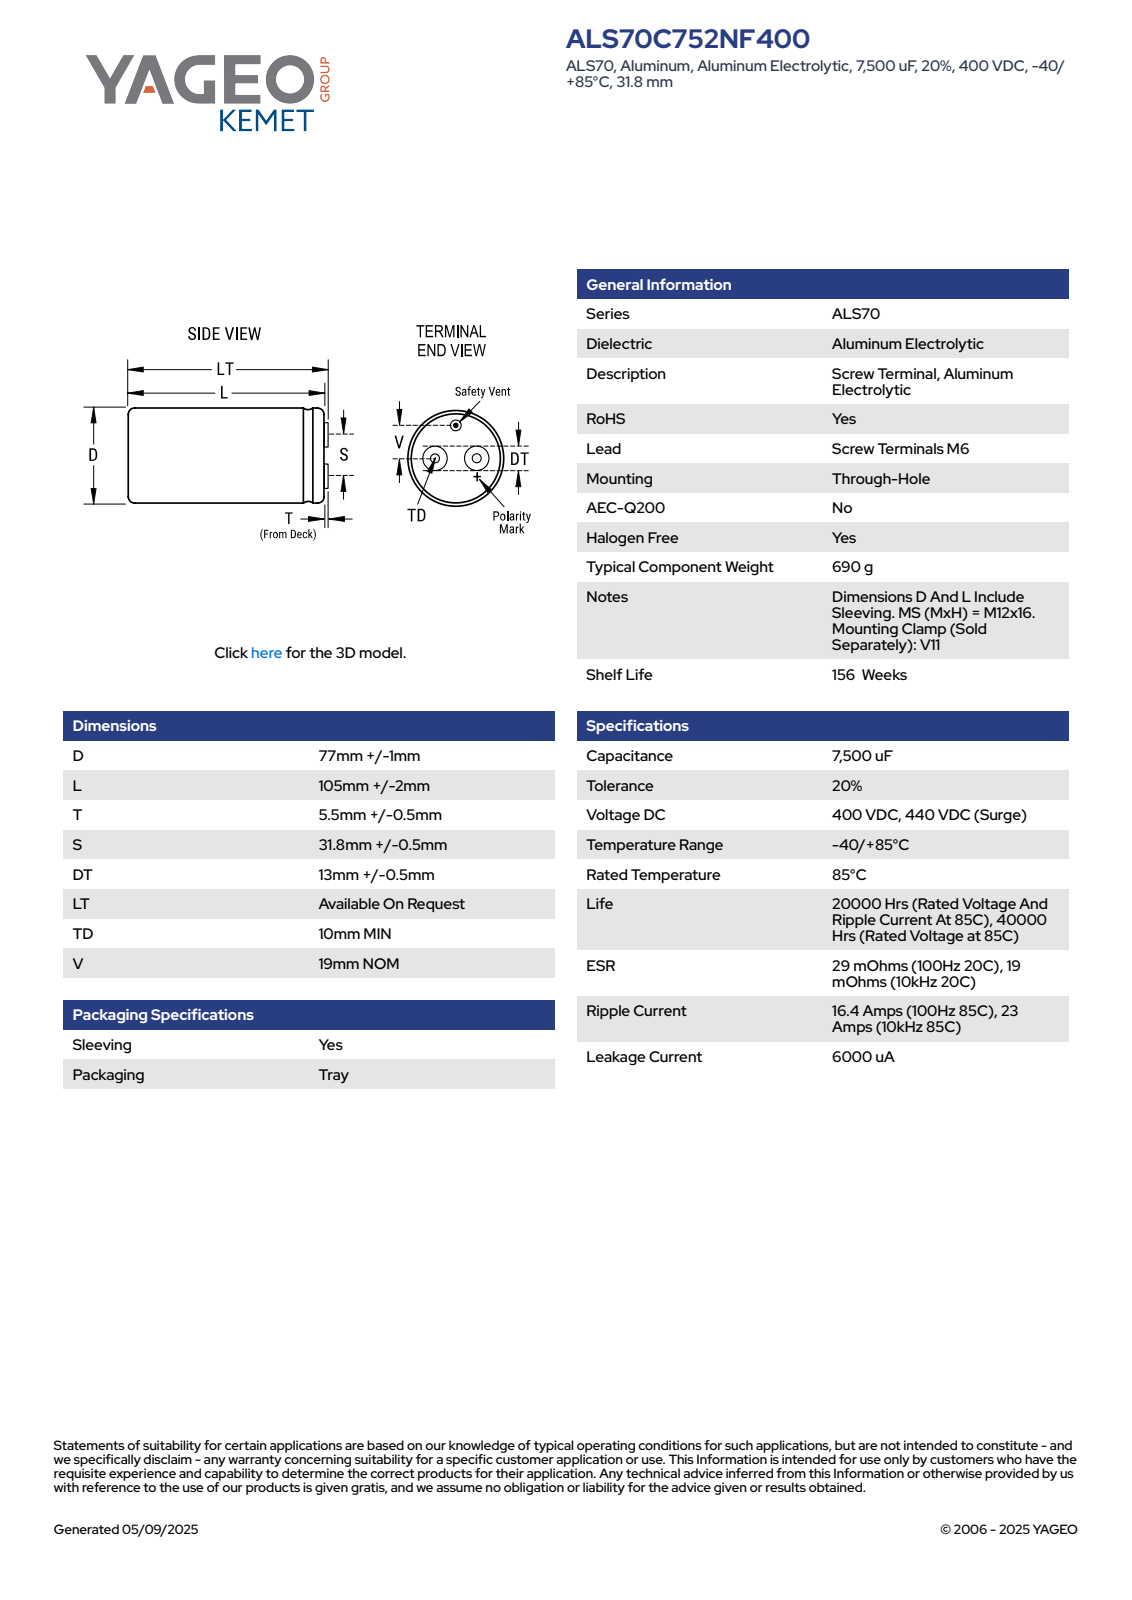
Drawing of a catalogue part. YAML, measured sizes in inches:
part_name: "CARC_KAR_77X105_D78L107T6S31.8DT13.500TD10.000V19.000"
step_written_by: "SolidWorks 2014 (AUTOMOTIVE_DESIGN)"
units: inches
bodies: {solids: 1, faces: 88, planar: 30, cylindrical: 19, other: 39}
overall_size: [4.449, 3.071, 3.071]
volume: 31.17
surface_area: 56.27
round_holes:
  - {diameter: 0.197, count: 2}
  - {diameter: 0.052, count: 1}
round_bosses_or_shafts:
  - {diameter: 0.531, count: 2}
  - {diameter: 3.071, count: 1}
  - {diameter: 0.089, count: 1}
partial_cylinders:
  - {radius: 1.536, count: 1}
face_to_face_distances: [4.213, 4.449, 0.236, 4.055, 0.157, 0.394, 4.226, 0.171, 0.014, 0.222]
hole_center_spacings: [0.976, 1.252]
